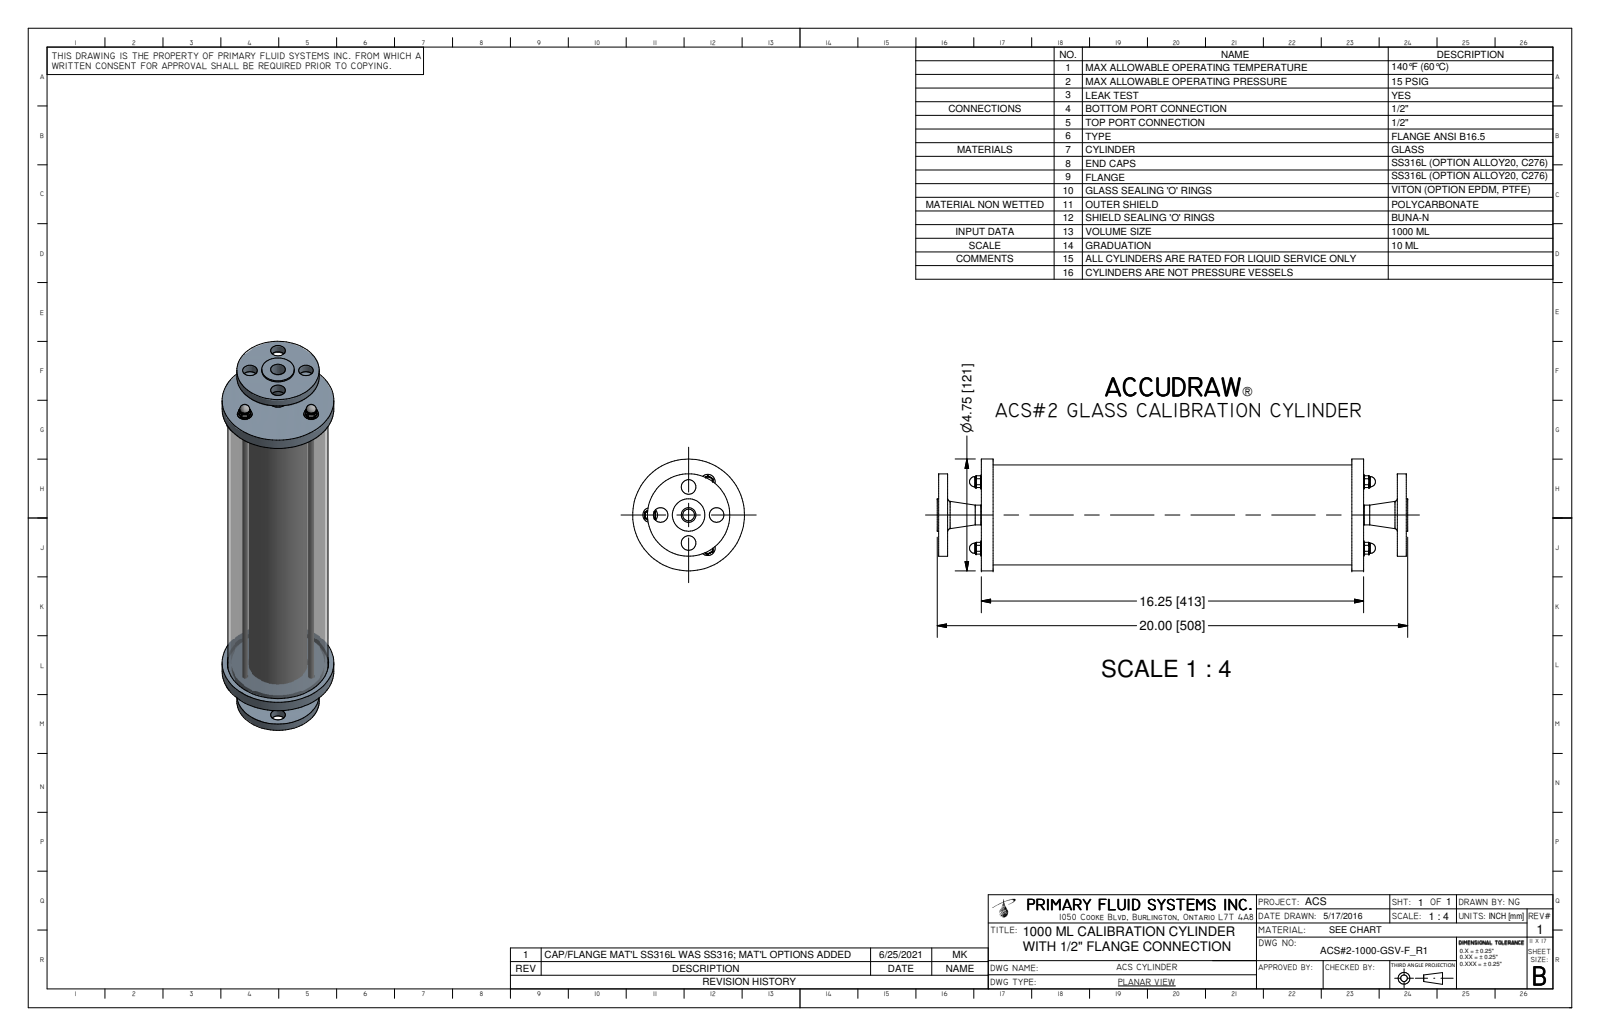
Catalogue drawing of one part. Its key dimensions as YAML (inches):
part_name: "ACS#2-1000-GSV-F_R0; ACS-3-1000-METAL-S_R1; ACS-2-1000-PC_R6; ACS-1-1000-A_R0 (+4 more)"
step_written_by: "Autodesk Inventor 2009 (AUTOMOTIVE_DESIGN)"
units: inches
bodies: {solids: 21, faces: 455, planar: 46, cylindrical: 57, other: 352}
overall_size: [19.995, 4.75, 4.75]
volume: 61.91
surface_area: 873.6
round_holes:
  - {diameter: 0.62, count: 4}
  - {diameter: 0.18, count: 3}
  - {diameter: 0.266, count: 3}
  - {diameter: 0.281, count: 3}
  - {diameter: 0.622, count: 1}
  - {diameter: 2.331, count: 1}
  - {diameter: 2.575, count: 1}
  - {diameter: 4, count: 1}
  - {diameter: 4.3, count: 1}
round_bosses_or_shafts:
  - {diameter: 0.625, count: 3}
  - {diameter: 0.25, count: 3}
  - {diameter: 4.75, count: 1}
  - {diameter: 4.25, count: 1}
  - {diameter: 3.95, count: 1}
  - {diameter: 3.5, count: 1}
  - {diameter: 2.519, count: 1}
  - {diameter: 2.2, count: 1}
face_to_face_distances: [0.5, 15.75, 16.25, 1.81, 2.31, 17.56, 18.06, 0.38, 19.49, 1.43]
hole_center_spacings: [1.19, 1.683, 1.631, 2.826, 0.846, 1.462, 2.019, 2.38]
